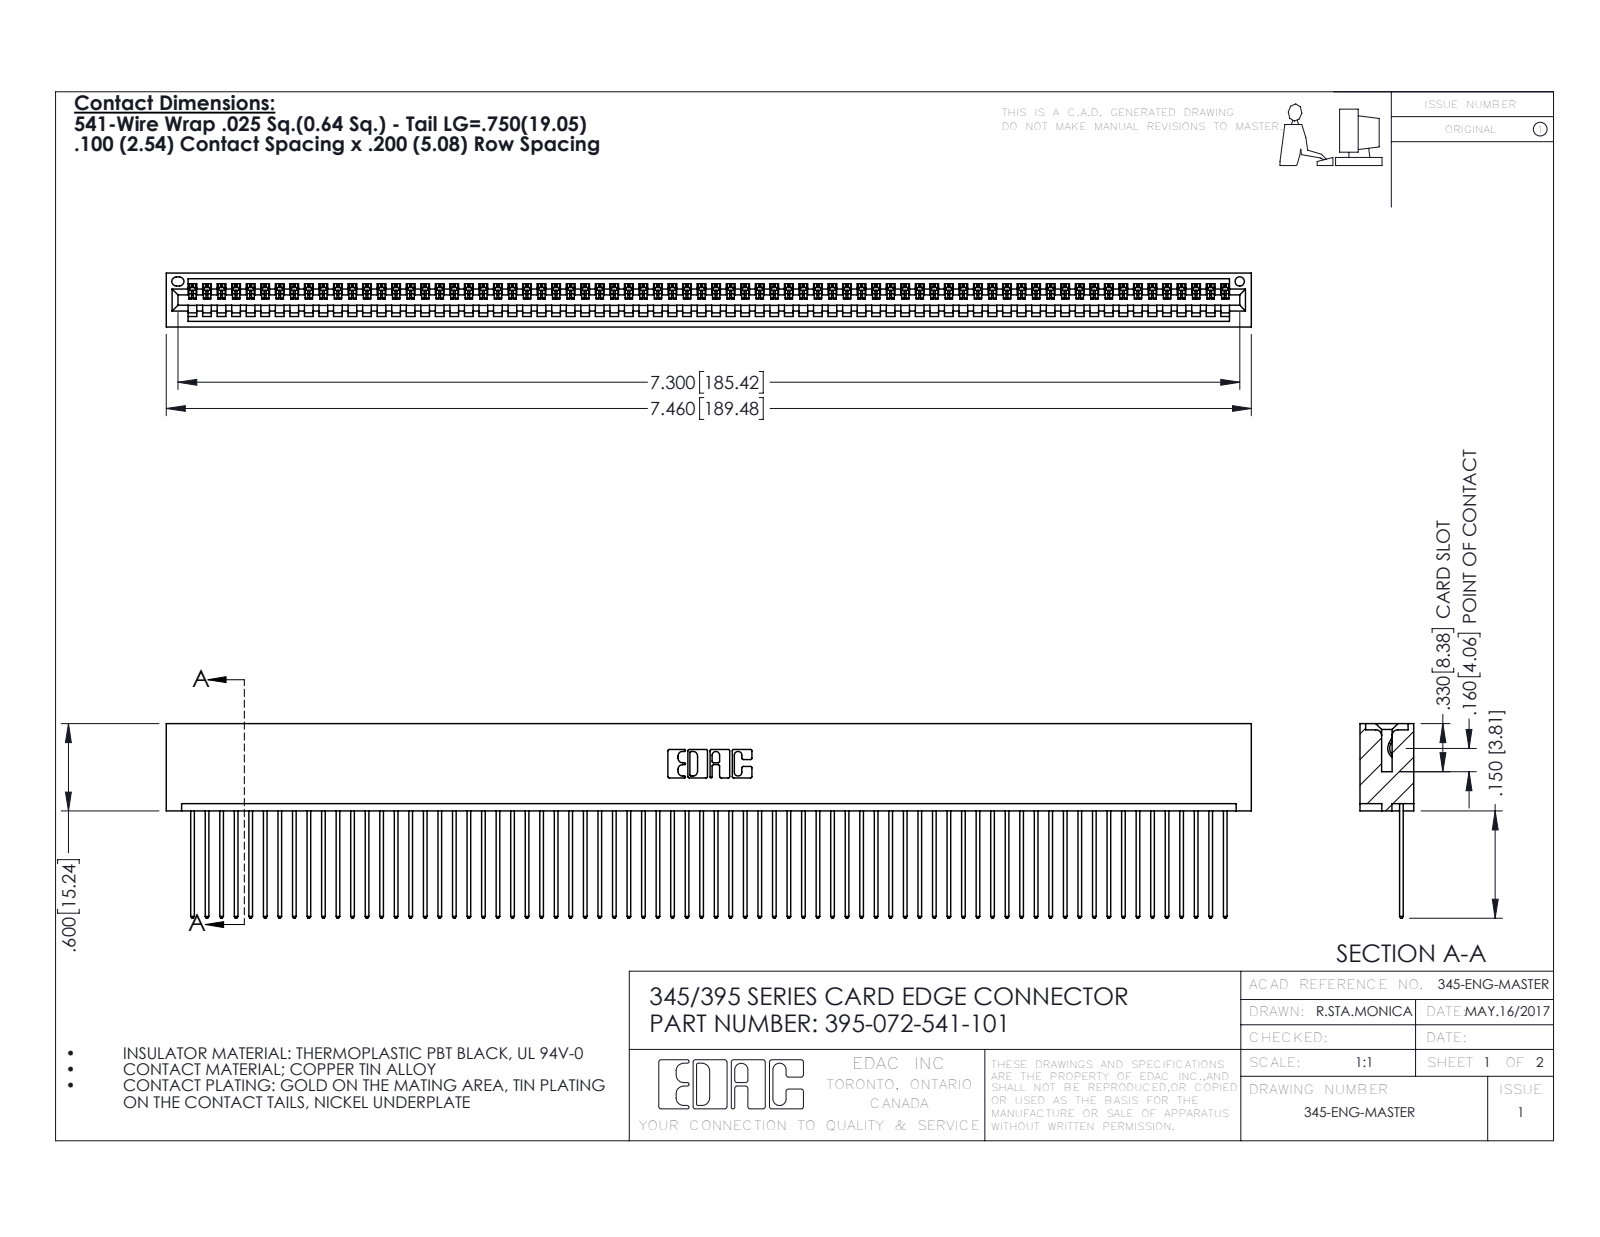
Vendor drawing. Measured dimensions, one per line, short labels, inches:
name: 345-292-001_345-293-141; 345 Part_No Mounting Lugs; 395-072-541-101
written by: SolidWorks 2016 (CONFIG_CONTROL_DESIGN)
unit: in
bodies: 73 solids, 4294 faces (2956 planar, 1338 cylindrical, 0 other)
size: 7.46 × 1.337 × 0.37
volume: 1.163 in³; area: 42.36 in²
holes: 1× ⌀0.064
rounds: 144× R0.006, 144× R0.01, 22× R0.01, 6× R0.007, 6× R0.031, 3× R0.026, 2× R0.031, 2× R0.04
face distances: 0.072, 0.298, 0.098, 0.272, 0.025, 0.37, 0.2, 0.225, 0.149, 0.072
